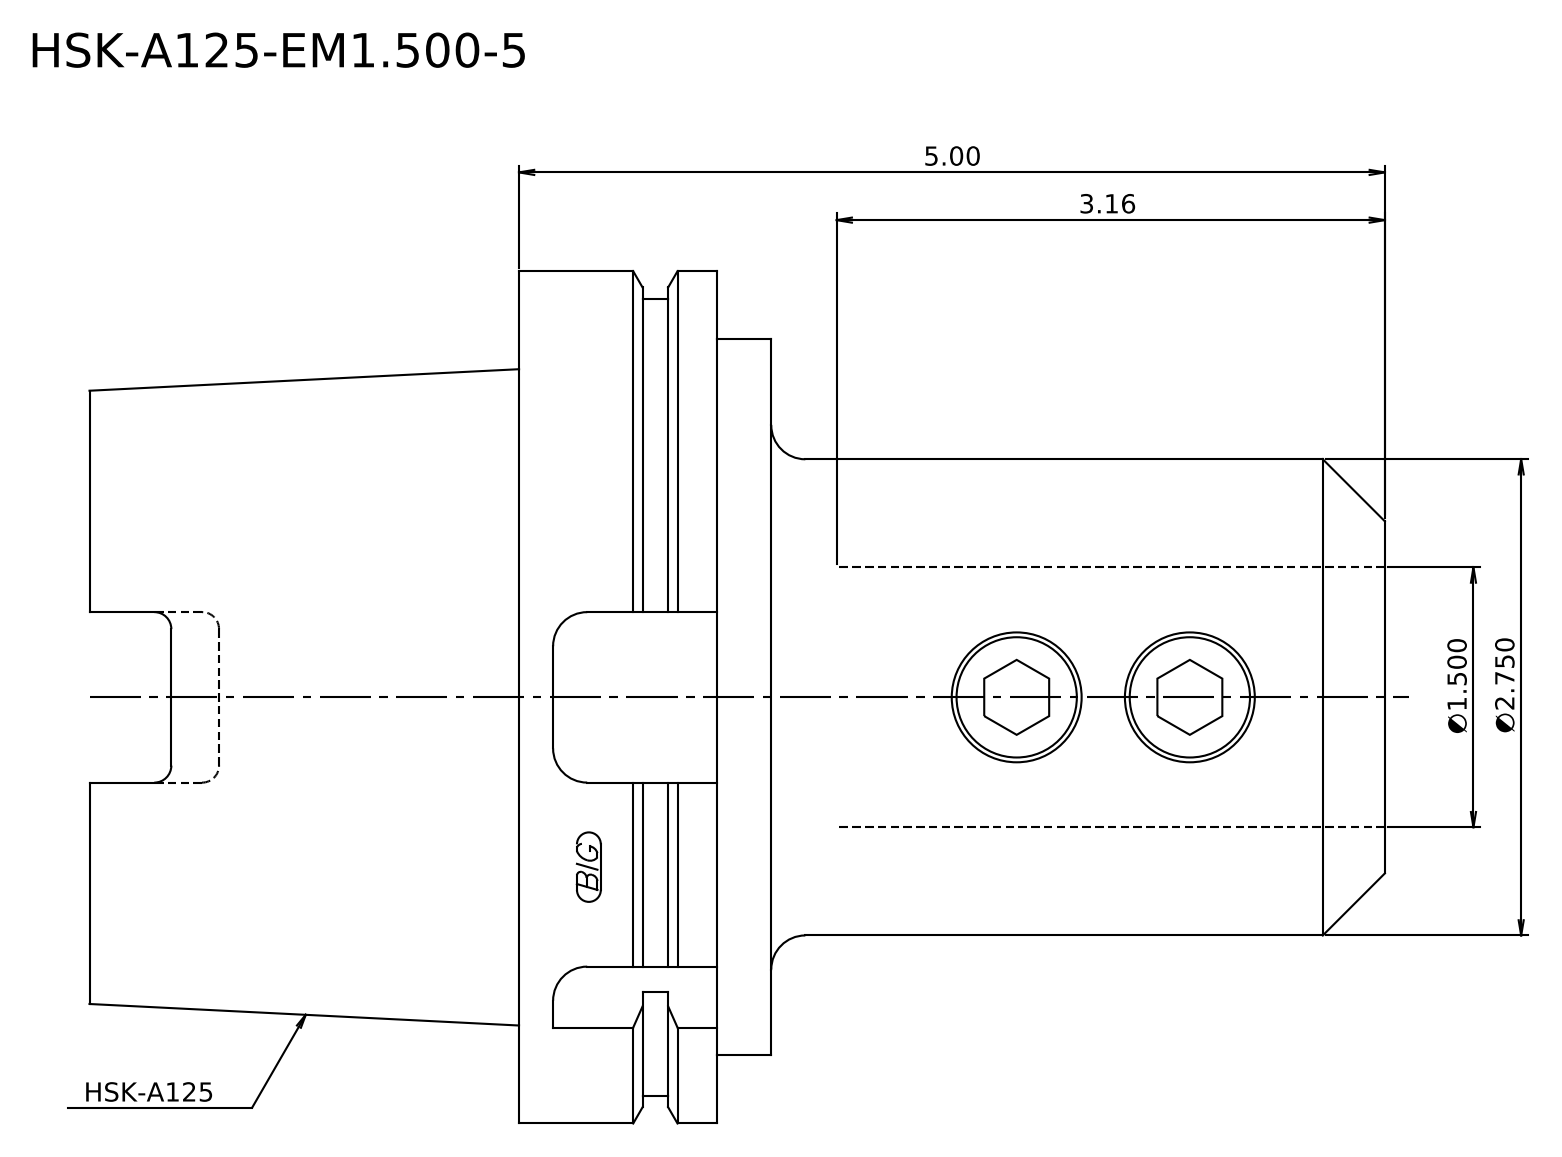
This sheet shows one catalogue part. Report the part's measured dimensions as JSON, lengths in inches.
{"step_written_by": "Kubotek KeyCreator 2011 V10.0.2 (22737) (automotive_design)", "units": "inches", "bodies": {"solids": 1, "faces": 17, "planar": 7, "cylindrical": 5, "other": 5}, "overall_size": [7.48, 4.921, 4.921], "volume_in3": 72.44, "surface_area_in2": 118, "round_bosses_or_shafts": [[4.921, 1], [4.606, 1], [4.134, 1], [2.75, 1]], "face_to_face_distances": [2.48, 1.457, 3.937, 0.315, 1.142, 3.622, 3.543, 3.858, 5, 7.48]}
